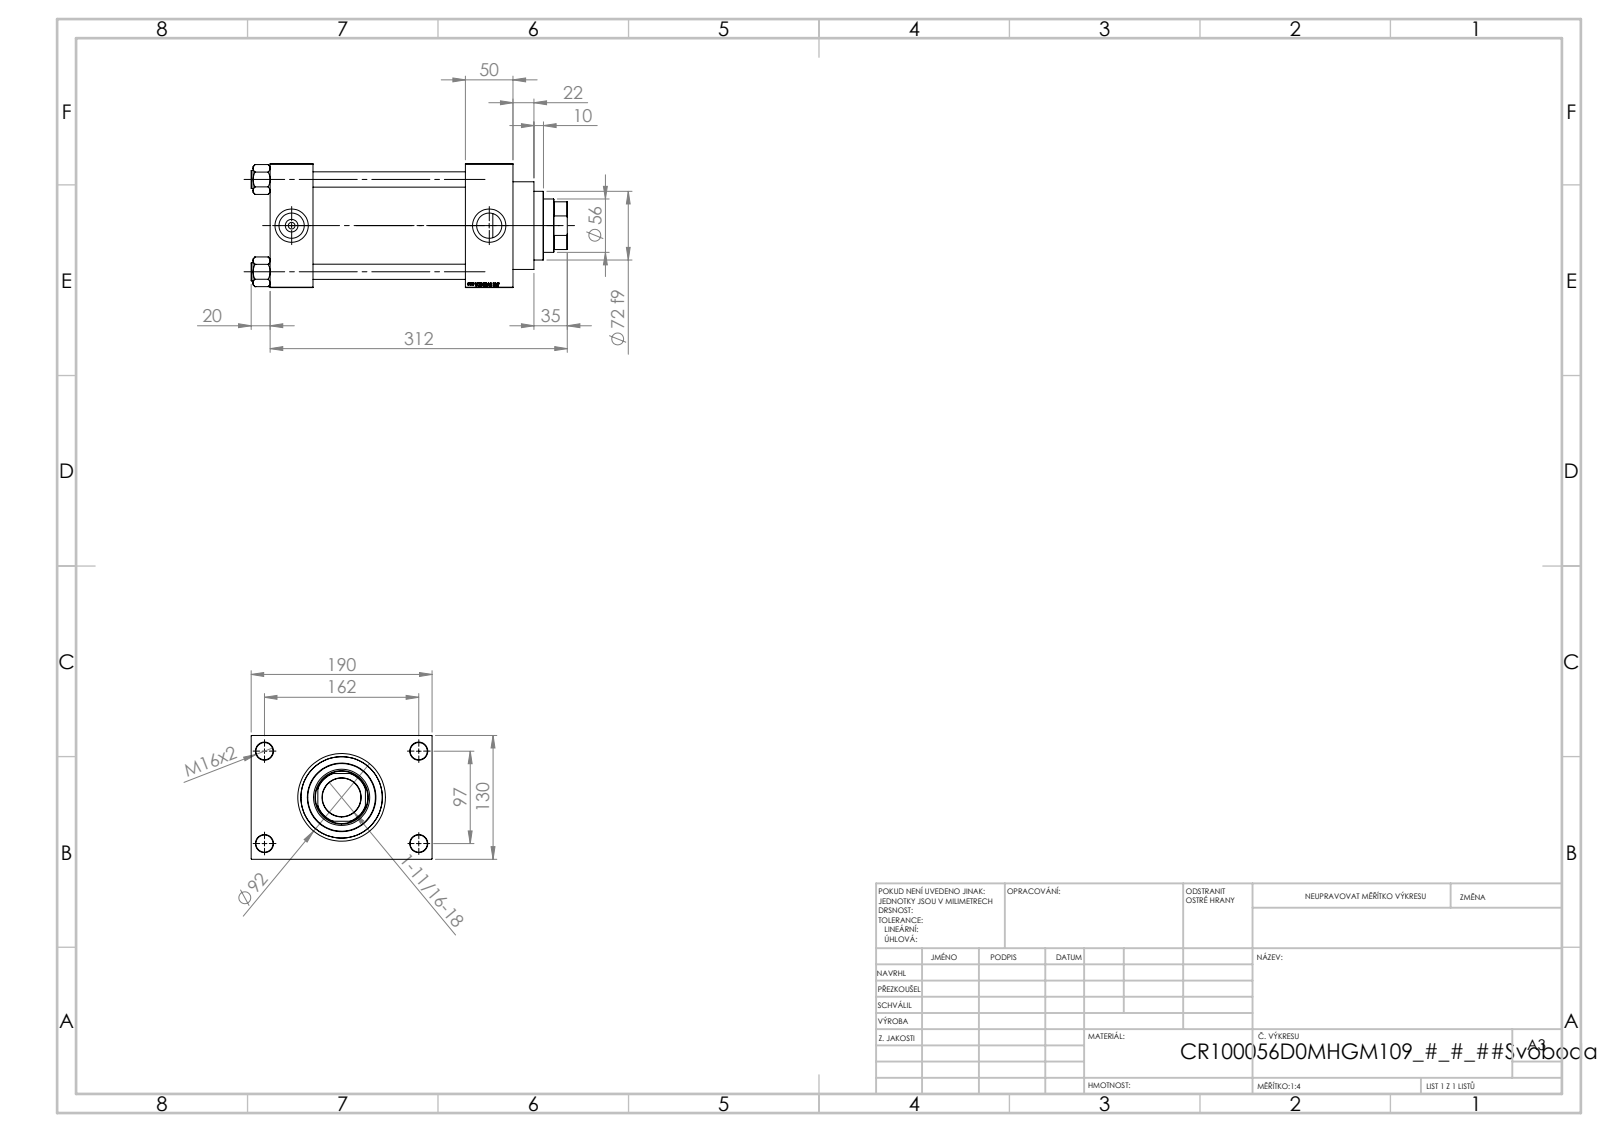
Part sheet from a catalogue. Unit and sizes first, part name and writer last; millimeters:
Units: millimetres
Overall size (bounding box): 332 × 190 × 130
Round holes (diameter × count): ⌀16 ×4, ⌀18 ×4, ⌀7 ×2, ⌀26.44 ×2, ⌀35 ×2, ⌀40.5 ×1, ⌀56 ×1, ⌀59 ×1, ⌀76 ×1, ⌀85.5 ×1, ⌀100 ×1
Round bosses / shafts (diameter × count): ⌀19 ×4, ⌀106 ×1, ⌀92 ×1, ⌀72 ×1
Partial cylindrical surfaces — rounded edges, fillets, slot ends (radius × count): R27 ×1
Main face-to-face distances: 160, 130, 50, 45, 205, 255, 210, 30, 190, 96
Hole centre spacings: 32.55, 68.52, 94.41, 96.9, 102.27, 129.45, 161.73, 97
Volume: 3 005 000 mm³ · Surface area: 453 513 mm²
Bodies: 11 solids, 1151 faces (545 planar, 88 cylindrical, 518 other)
Part name (STEP PRODUCT): V215CR_VCP_D; V215CR_D_Body; V215CR_D_TYCINKA; NUT_M5_D (+1 more)
STEP written by: SolidWorks 2019 (CONFIG_CONTROL_DESIGN)
